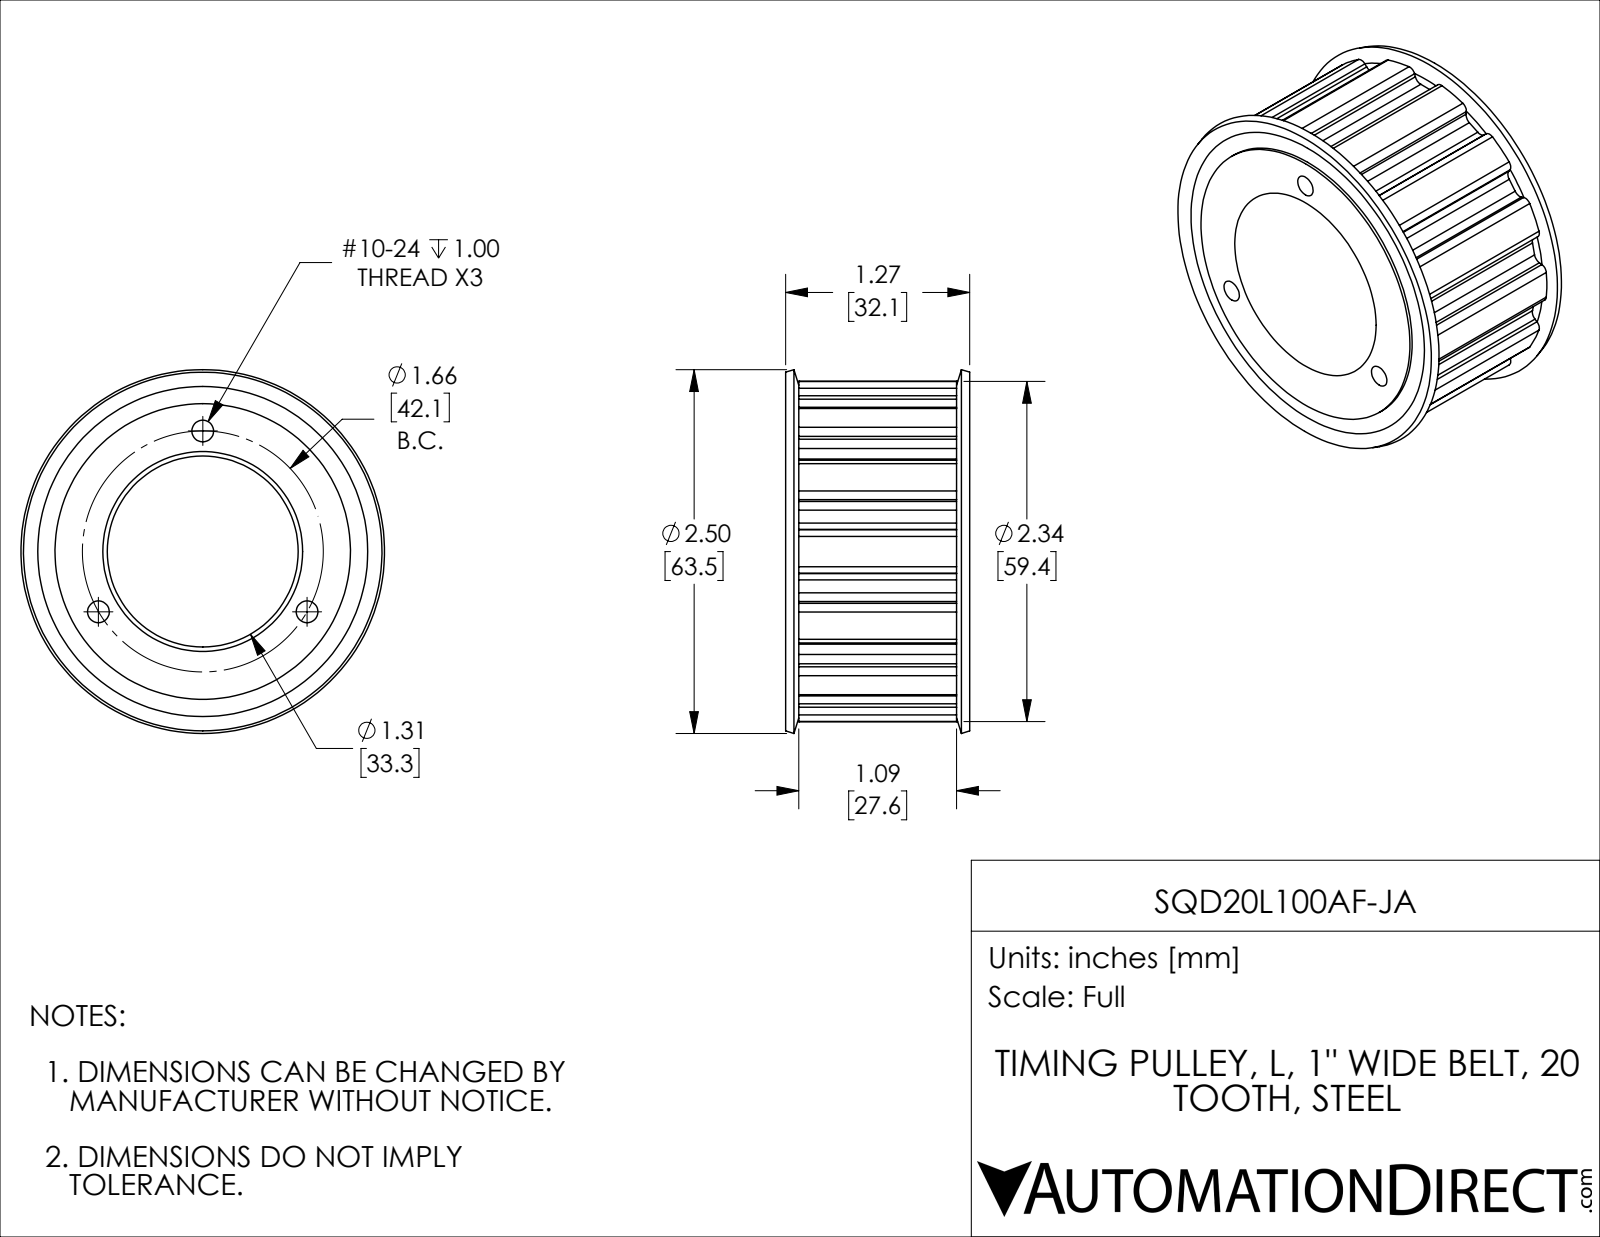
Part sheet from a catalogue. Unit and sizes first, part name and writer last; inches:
Units: inches
Overall size (bounding box): 2.5 × 2.5 × 1.265
Round holes (diameter × count): ⌀0.15 ×3, ⌀1.312 ×1
Round bosses / shafts (diameter × count): ⌀2.031 ×1
Partial cylindrical surfaces — rounded edges, fillets, slot ends (radius × count): R0.05 ×28, R0.056 ×28, R1.179 ×1
Main face-to-face distances: 1.25, 0.022, 1.228, 1.205, 0.082, 0.06, 1.145, 1.168, 1.167, 1.145
Hole centre spacings: 0.828, 1.434, 0.828, 1.435
Volume: 3.357 in³ · Surface area: 26.18 in²
Bodies: 1 solid, 214 faces (102 planar, 92 cylindrical, 20 other)
Part name (STEP PRODUCT): SQD20L100AF-JA
STEP written by: SolidWorks 2019 (CONFIG_CONTROL_DESIGN)
